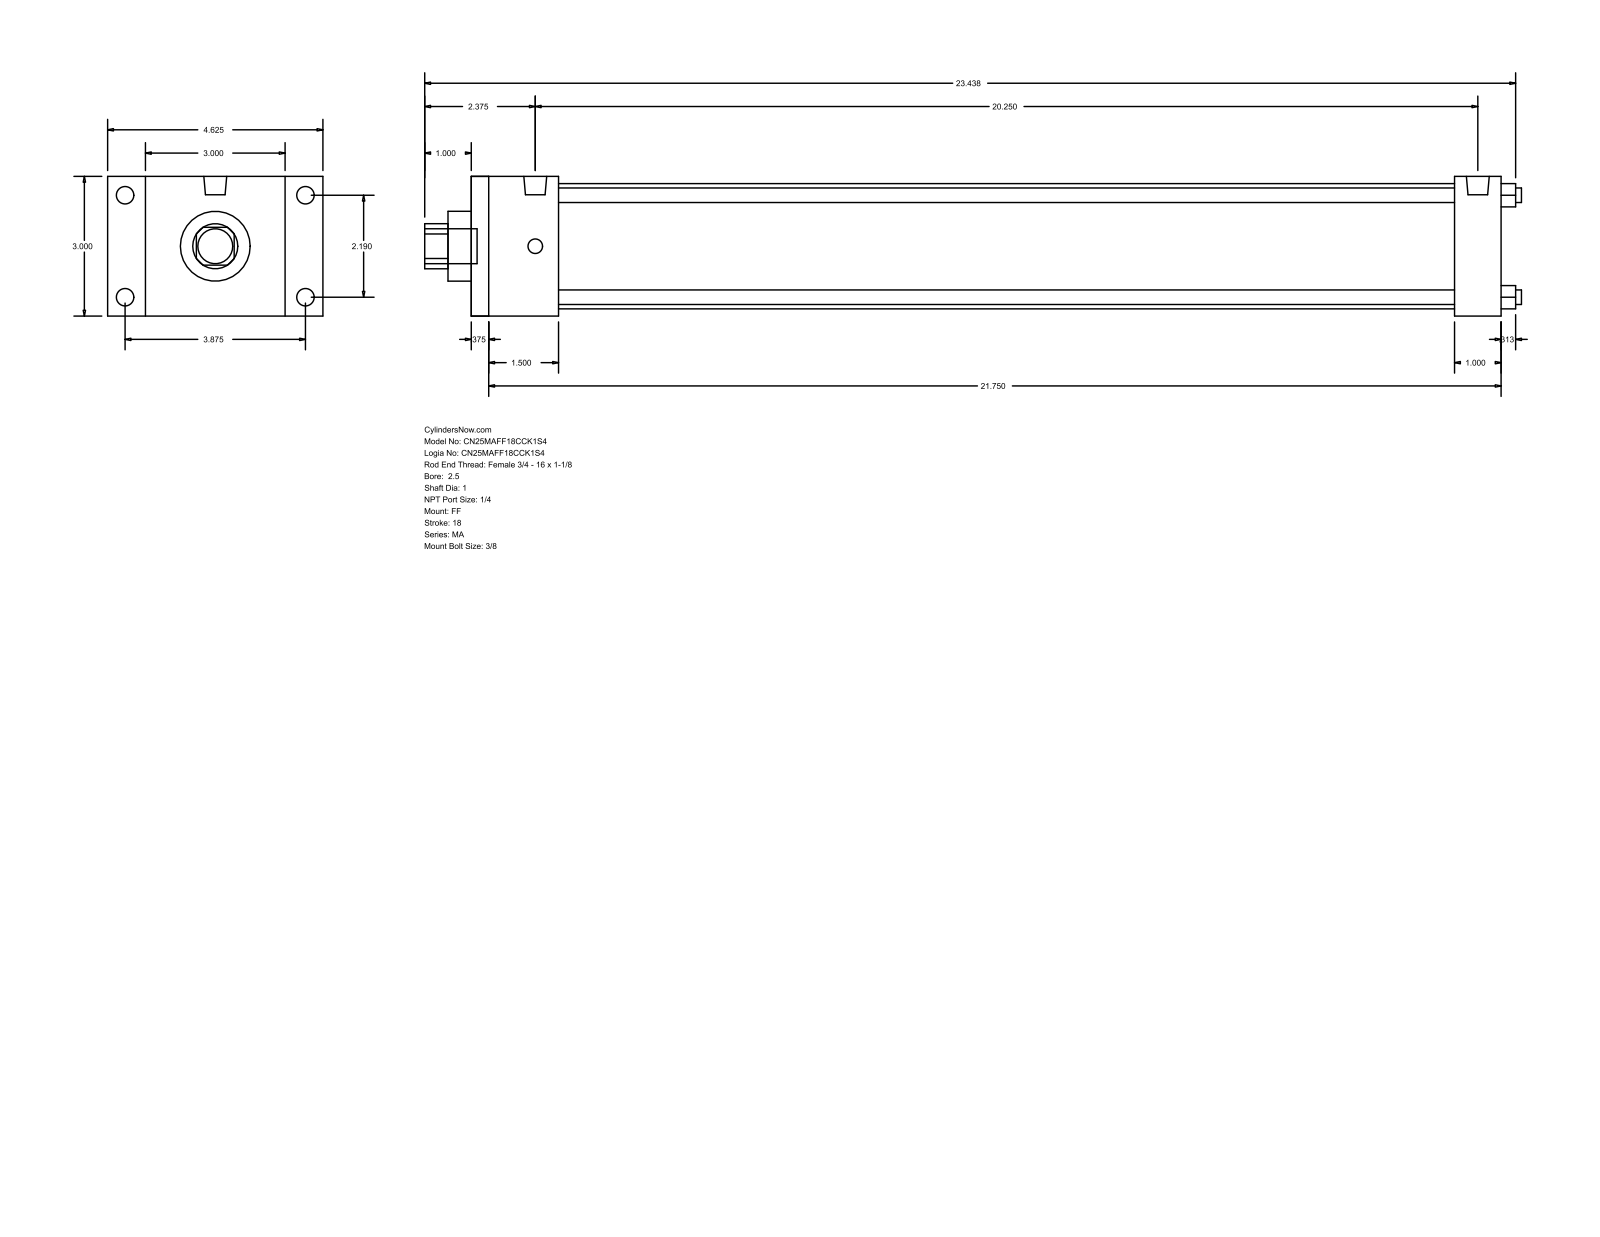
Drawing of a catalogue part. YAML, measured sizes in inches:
part_name: "MA_FF__0250_1"
step_written_by: "GSSL Pune (CONFIG_CONTROL_DESIGN)"
units: inches
bodies: {solids: 0, faces: 92, planar: 64, cylindrical: 28, other: 0}
overall_size: [23.563, 4.625, 3]
round_holes:
  - {diameter: 0.313, count: 4}
  - {diameter: 1, count: 1}
  - {diameter: 1.5, count: 1}
  - {diameter: 2.69, count: 1}
round_bosses_or_shafts:
  - {diameter: 0.375, count: 4}
  - {diameter: 0.313, count: 4}
  - {diameter: 0.492, count: 2}
  - {diameter: 0.75, count: 1}
partial_cylinders:
  - {radius: 0.484, count: 1}
face_to_face_distances: [3, 22.125, 0.375, 21.75, 1, 1.875, 21.125, 1.5, 20.75, 19.25]
hole_center_spacings: [1.548, 2.19, 3.097]
